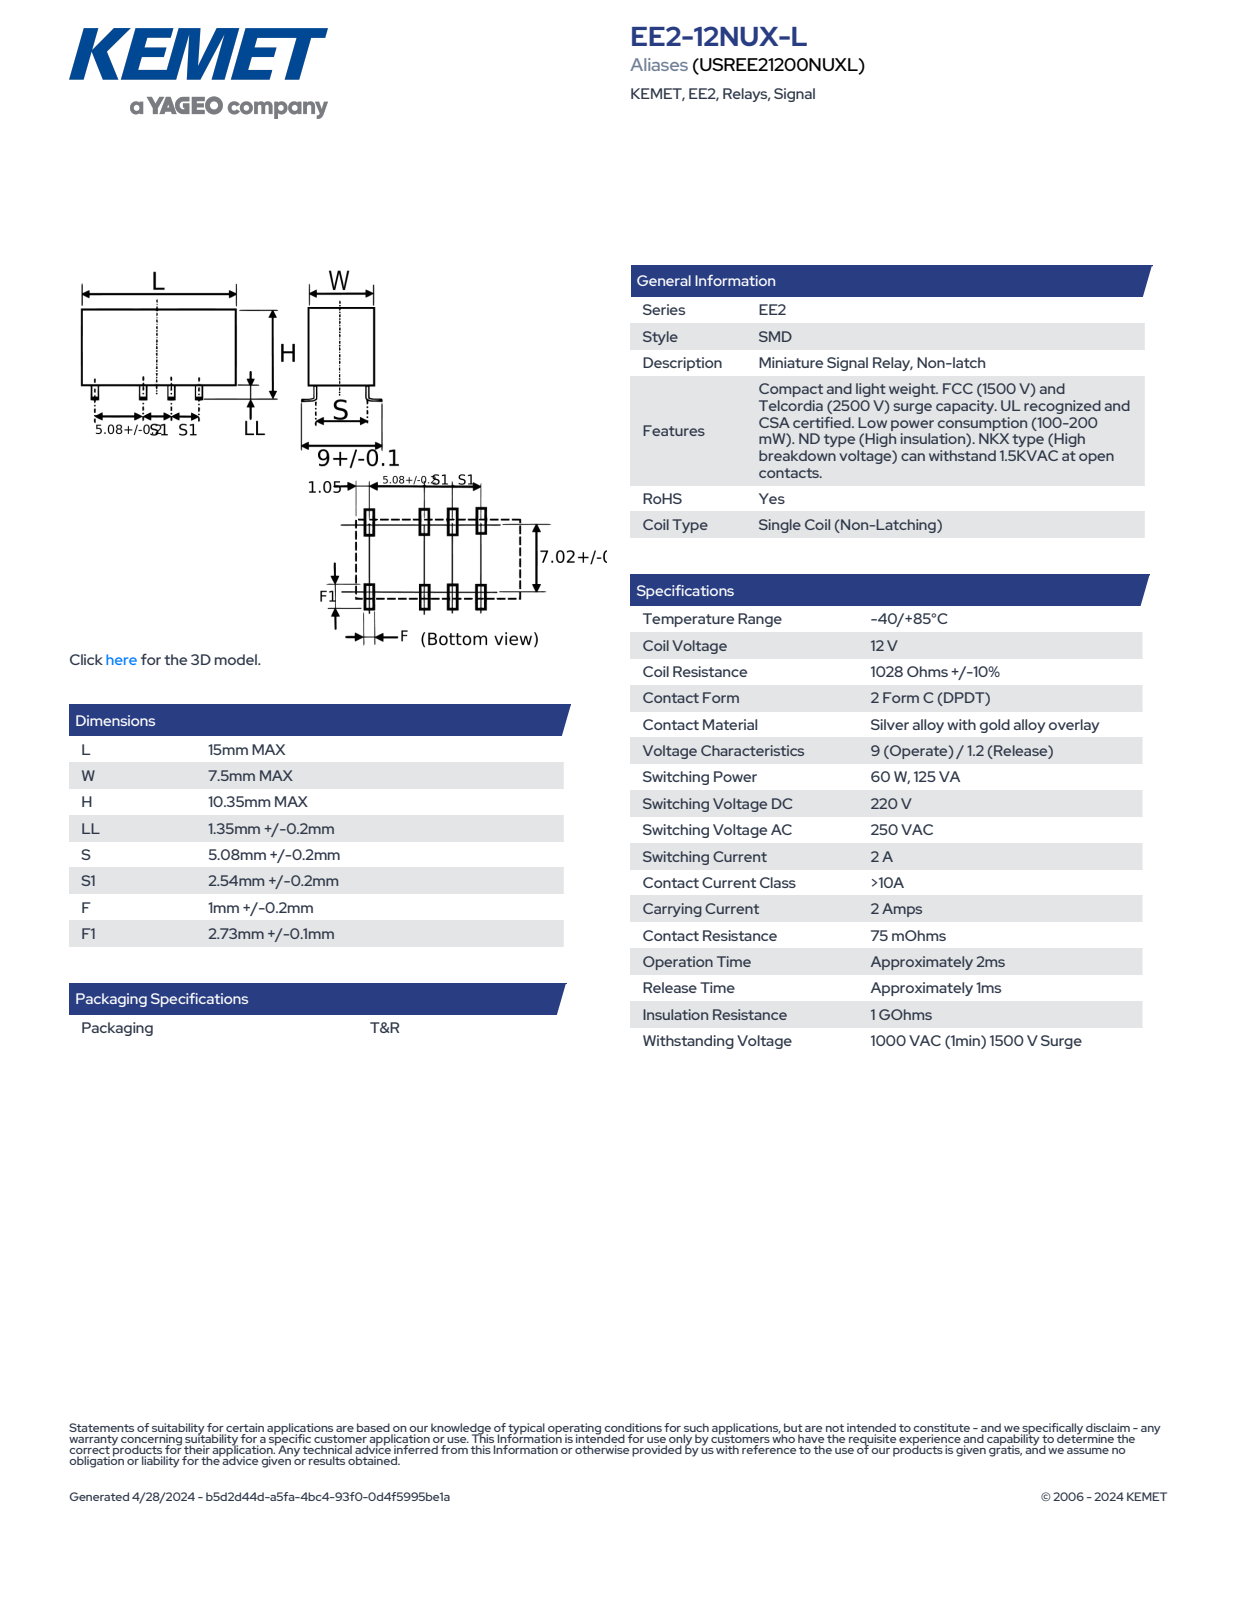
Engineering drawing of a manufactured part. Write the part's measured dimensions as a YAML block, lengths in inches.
part_name: "IR_TEE2HS_L15W7.5H10.35"
step_written_by: "SolidWorks 2014 (AUTOMOTIVE_DESIGN)"
units: inches
bodies: {solids: 1, faces: 116, planar: 116, cylindrical: 0, other: 0}
overall_size: [0.591, 0.408, 0.354]
volume: 0.061
surface_area: 1.03
face_to_face_distances: [0.295, 0.346, 0.591, 0.051, 0.061, 0.407, 0.398, 0.02, 0.2, 0.1]
